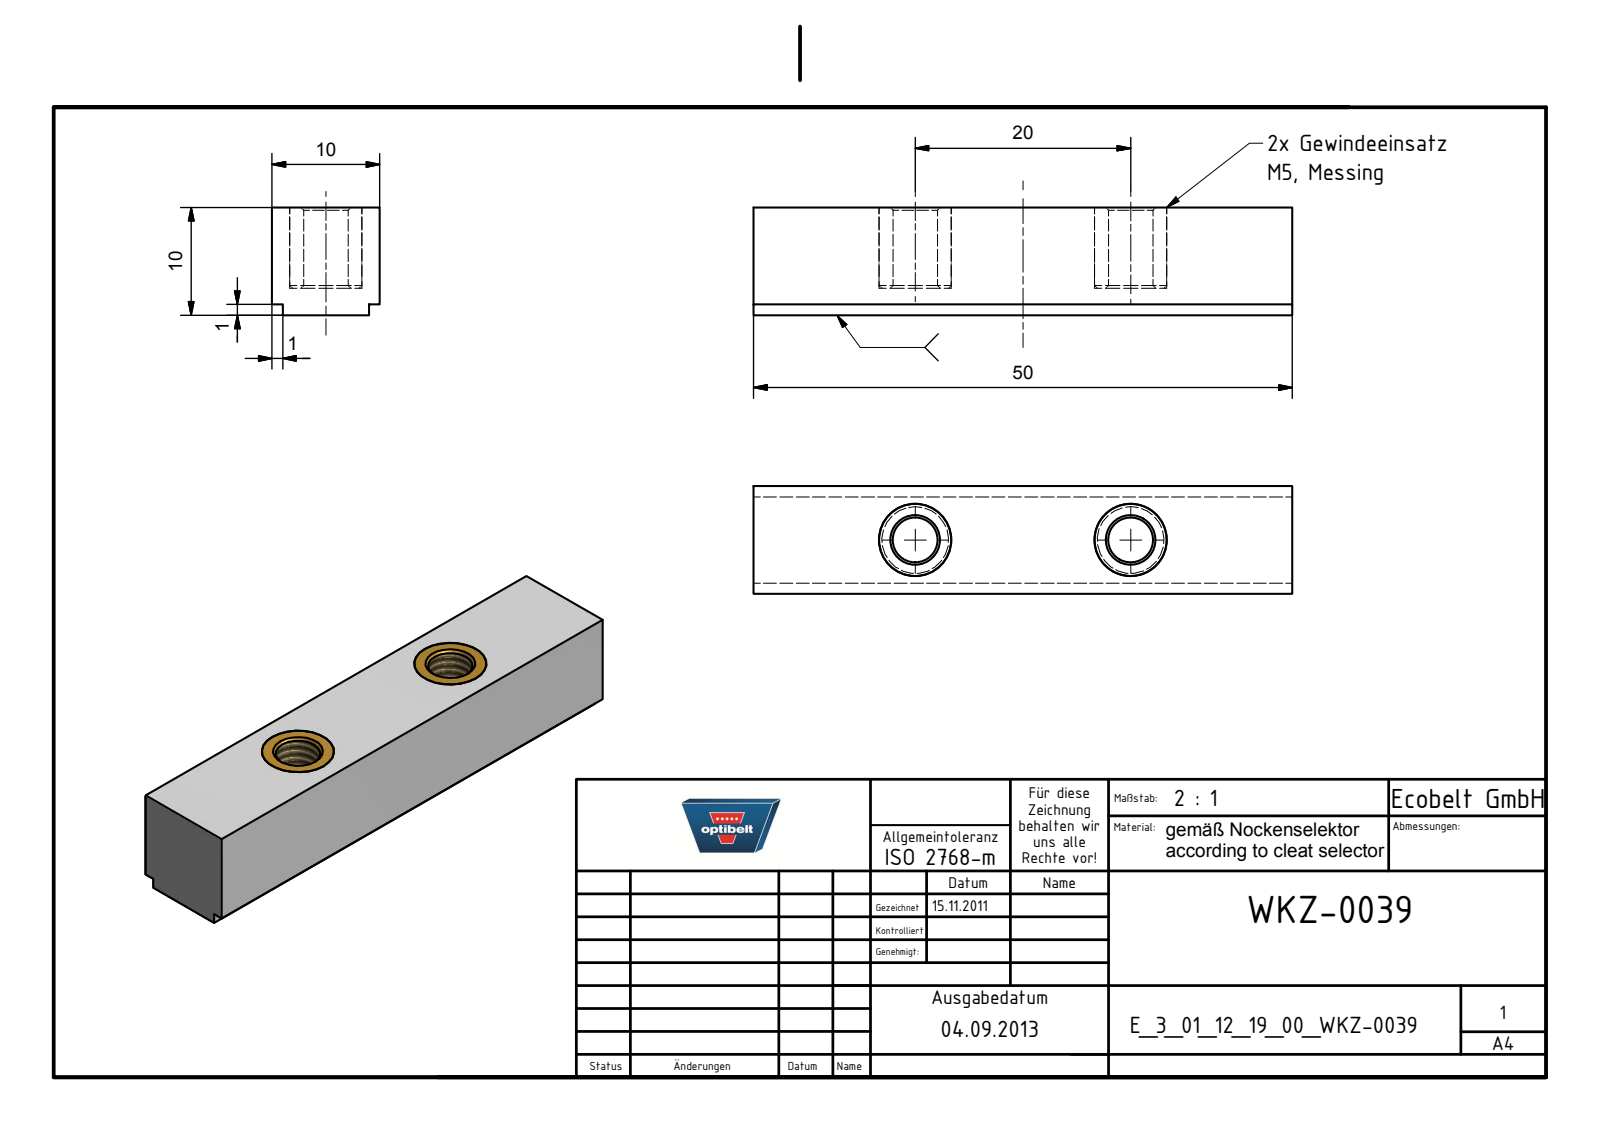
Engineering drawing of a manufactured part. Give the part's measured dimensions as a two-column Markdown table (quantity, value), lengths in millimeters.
| quantity | value |
| --- | --- |
| part name | E_3_01_12_19_00_WKZ-0039; E_3_01_12_19_00_WKZ-0039_Teil1; E_3_01_12_19_00_WKZ-0039_Teil2 |
| STEP written by | Autodesk Inventor 2018 (AUTOMOTIVE_DESIGN) |
| units | millimeters |
| bodies | 3 solids, 28 faces (16 planar, 6 cylindrical, 6 other) |
| overall size | 50 × 10 × 10 |
| volume | 4 696 mm³ |
| surface area | 3 096 mm² |
| round holes (diameter × count) | 4.13 × 2, 6.7 × 2 |
| main face-to-face distances | 10, 1, 9, 50, 2.5, 1.5, 7.5, 8 |
| hole center spacings | 20 |
